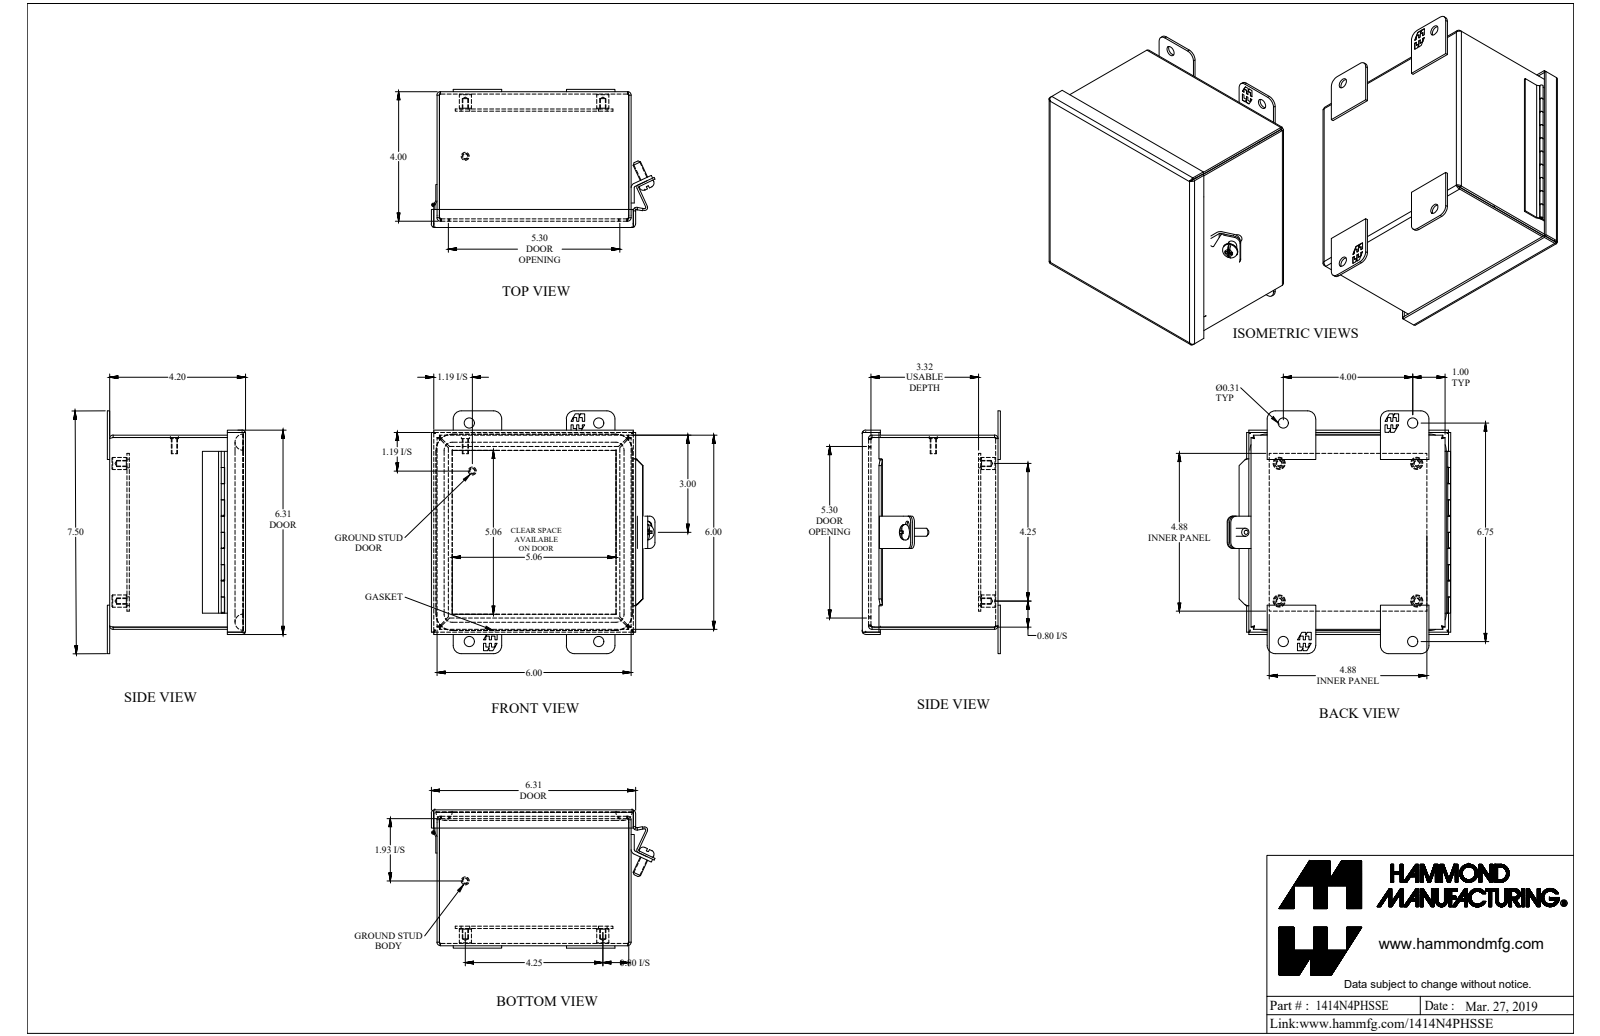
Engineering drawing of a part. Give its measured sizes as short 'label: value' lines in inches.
name: 1414N4PHSSE
written by: SolidWorks 2018 (AUTOMOTIVE_DESIGN)
unit: in
bodies: 19 solids, 556 faces (358 planar, 141 cylindrical, 57 other)
size: 7.5 × 6.903 × 4.269
volume: 18.45 in³; area: 520.5 in²
holes: 4× ⌀0.156, 4× ⌀0.265, 4× ⌀0.313, 1× ⌀0.05, 1× ⌀0.213
bosses: 4× ⌀0.375, 3× ⌀0.25, 2× ⌀0.19, 1× ⌀0.48, 1× ⌀0.1, 1× ⌀0.045
rounds: 24× R0.25, 9× R0.036, 9× R0.108, 4× R0.007, 4× R0.046, 4× R0.079, 4× R0.118, 4× R0.188
face distances: 0.072, 5.928, 4.125, 3.593, 0.532, 5.856, 4.197, 6, 4.053, 0.604
hole spacings: 4.25, 4.25, 4.31, 1.256, 5.502, 6.01, 6.875, 1.257
